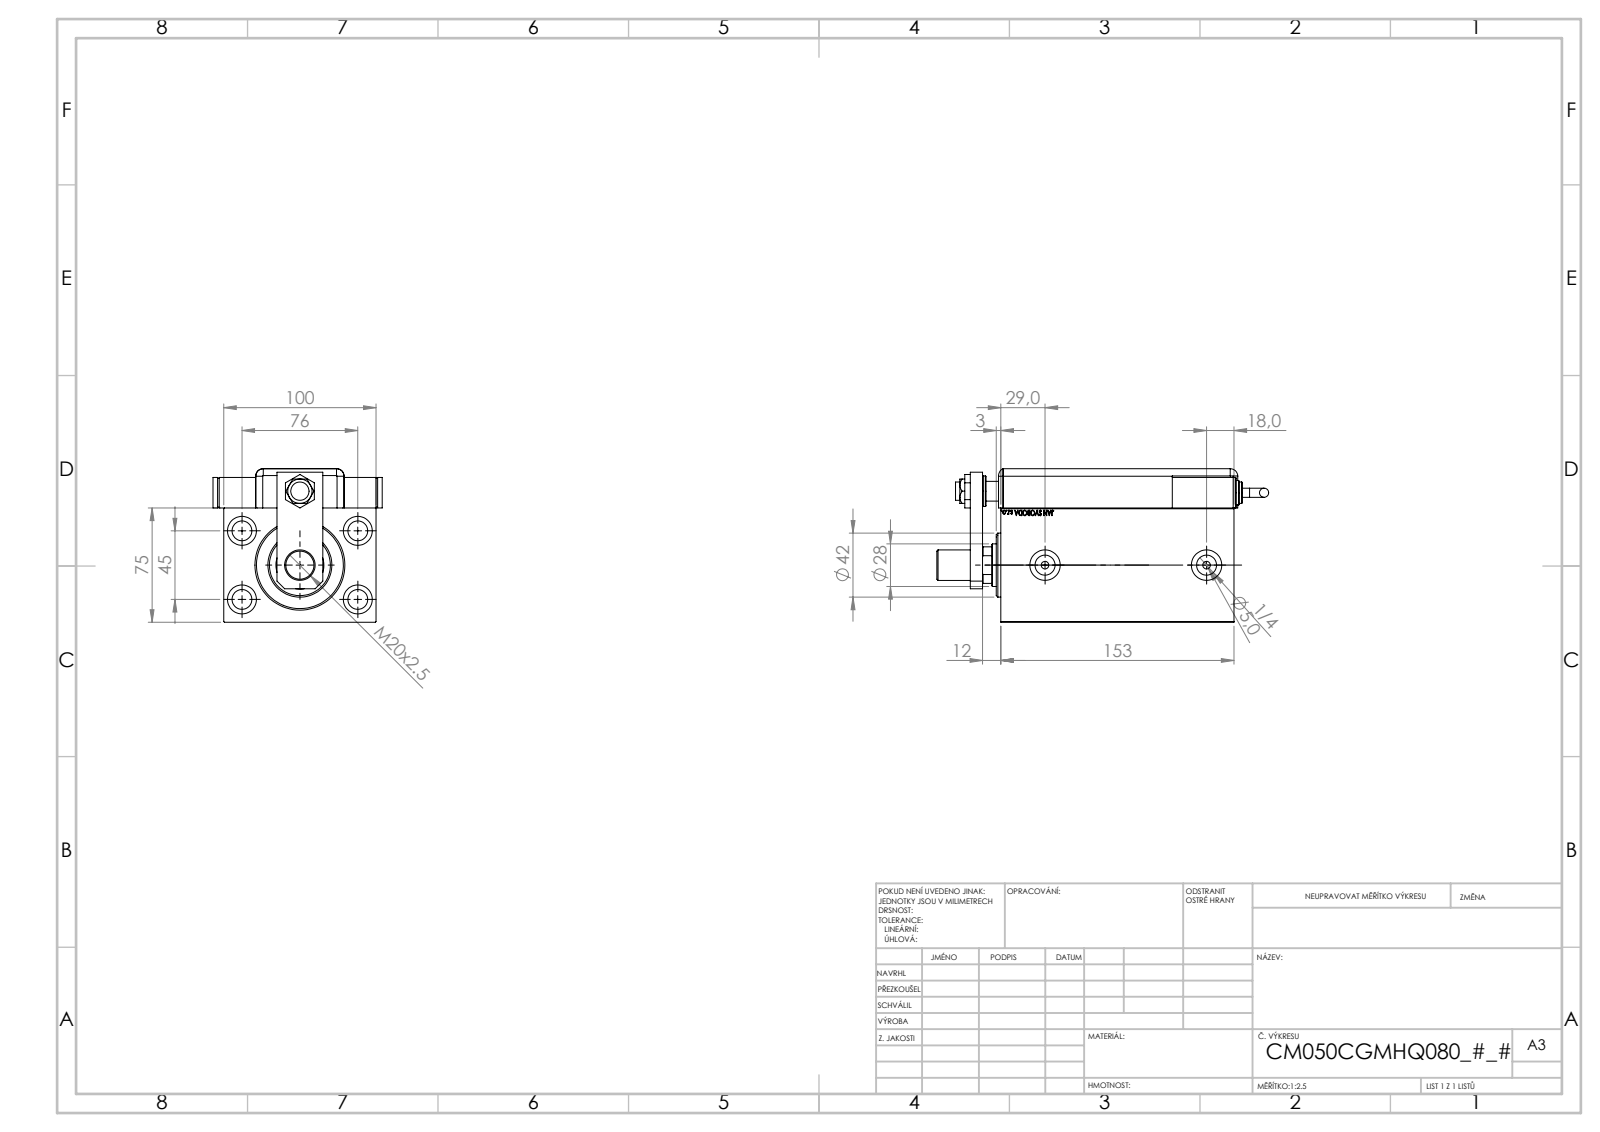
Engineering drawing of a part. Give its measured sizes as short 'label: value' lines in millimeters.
name: SWITCH DIM A_G; TYC; NUT_D19; V450CM_C_VCP (+7 more)
written by: SolidWorks 2019 (CONFIG_CONTROL_DESIGN)
unit: mm
bodies: 14 solids, 1263 faces (619 planar, 121 cylindrical, 523 other)
size: 217.76 × 111 × 100.8
volume: 1 117 000 mm³; area: 221 068 mm²
holes: 5× ⌀13, 4× ⌀19, 3× ⌀20, 2× ⌀4, 2× ⌀5, 2× ⌀8, 2× ⌀13.16, 1× ⌀12, 1× ⌀14, 1× ⌀18.5, 1× ⌀28, 1× ⌀31.5
bosses: 3× ⌀20, 2× ⌀16, 2× ⌀14, 2× ⌀6, 1× ⌀42, 1× ⌀18
rounds: 9× R5, 1× R10, 1× R13.5
face distances: 75, 3, 100, 25.8, 100.8, 97.8, 22.8, 14, 20, 2.8
hole spacings: 44.16, 45, 46.04, 76, 80.53, 88.32, 20, 48.5
